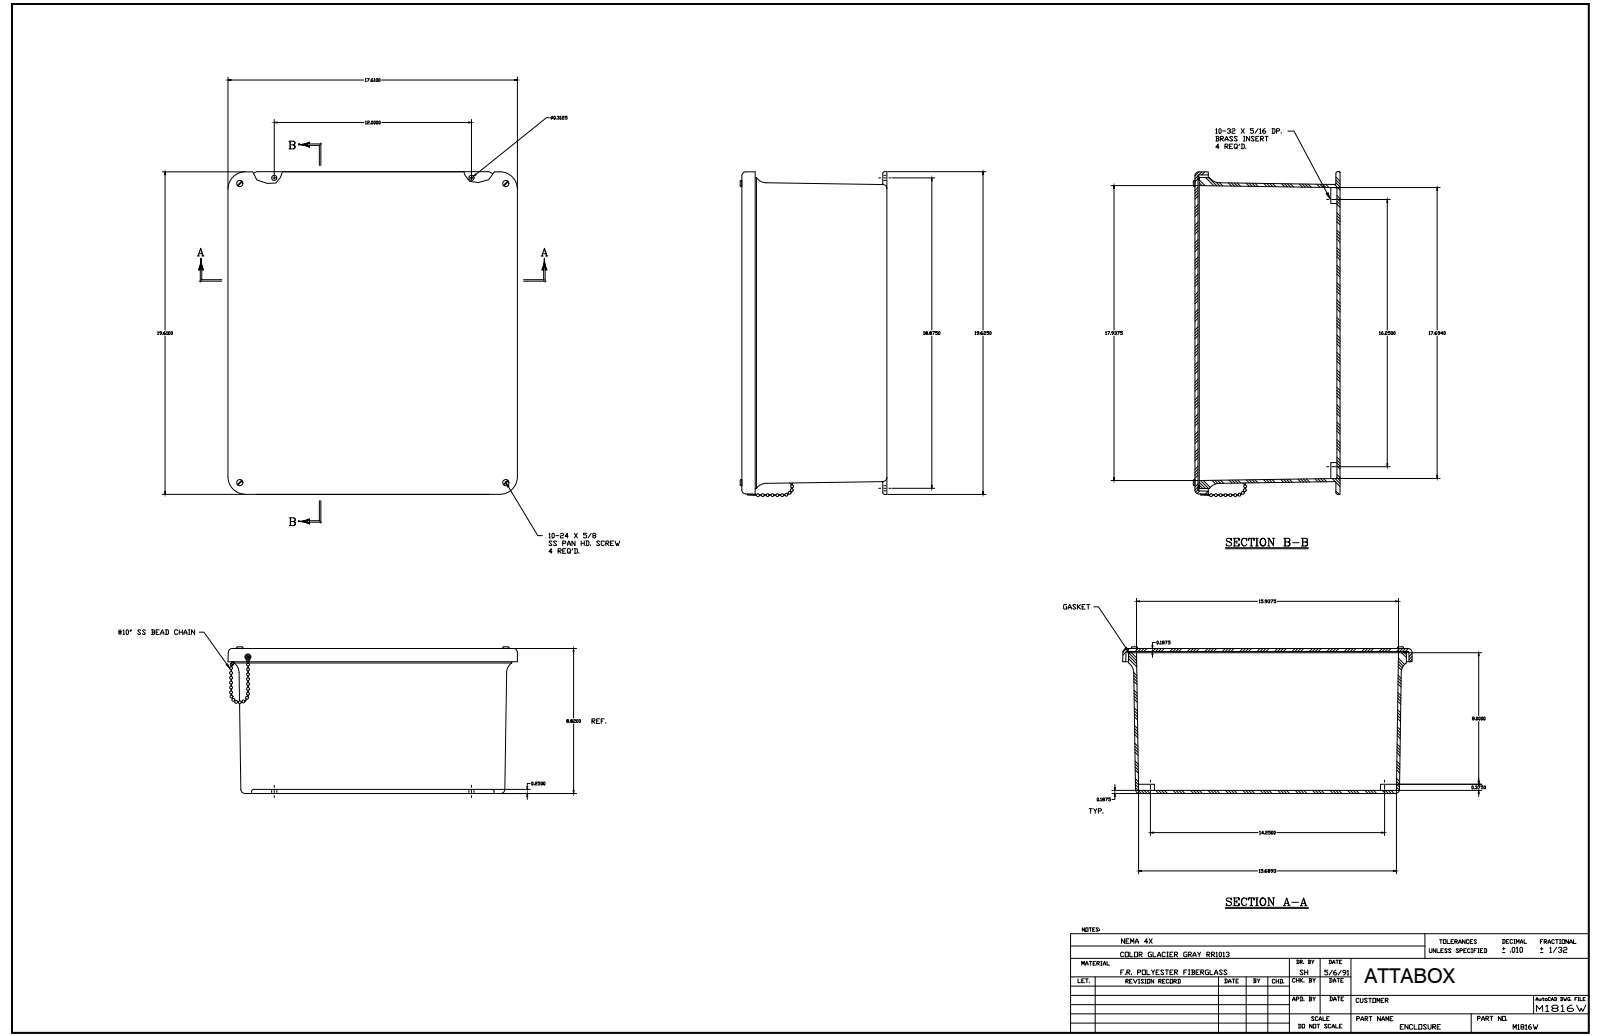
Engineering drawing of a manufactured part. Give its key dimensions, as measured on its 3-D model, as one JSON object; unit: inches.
{"part_name": "M1816W", "step_written_by": "SolidWorks 2018 (AUTOMOTIVE_DESIGN)", "units": "inches", "bodies": {"solids": 45, "faces": 891, "planar": 189, "cylindrical": 289, "other": 413}, "overall_size": [20.144, 17.765, 8.943], "volume_in3": 258.8, "surface_area_in2": 2648, "round_holes": [[0.14, 7], [0.152, 5], [0.145, 4], [0.156, 4], [0.218, 4], [0.187, 2], [0.126, 1]], "round_bosses_or_shafts": [[0.27, 8], [0.19, 4], [0.156, 4], [0.25, 2], [0.125, 2], [0.375, 1], [0.375, 1], [0.283, 1]], "partial_cylinders_radius": [[0.031, 20], [0.125, 12], [0.2, 8], [0.25, 8], [0.375, 4], [0.75, 4], [0.01, 2], [0.063, 2]], "face_to_face_distances": [0.188, 8.624, 0.187, 8.812, 8.437, 0.49, 0.302, 0.25, 8.563, 8.375], "hole_center_spacings": [1.37, 15.249, 17.246, 22.98, 3.375, 3.375, 6.375, 6.75]}
